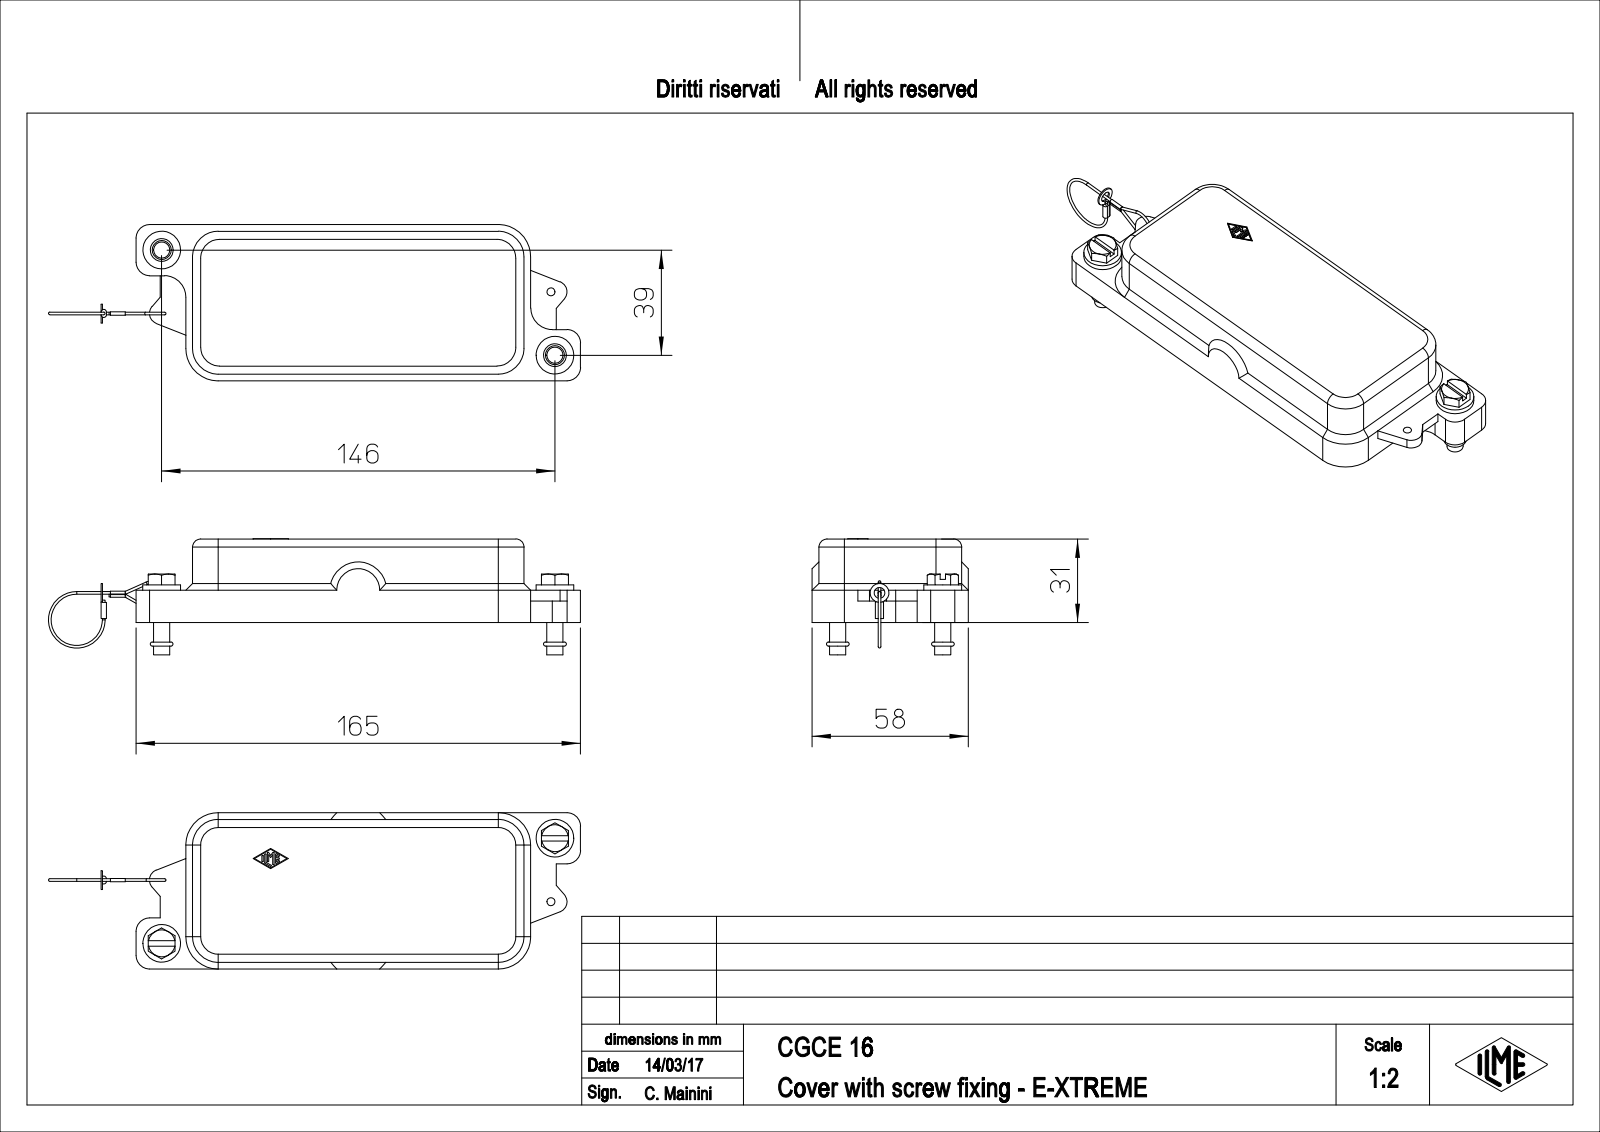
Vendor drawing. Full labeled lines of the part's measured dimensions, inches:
Part name (STEP PRODUCT): CGCE_16
STEP written by: PTC Creo Elements/Direct Modeling 19.0E 27-Jun-2016 (C) Parametric Technology GmbH (AUTOMOTIVE_DESIGN)
Units: inches
Bodies: 1 solid, 247 faces (124 planar, 87 cylindrical, 36 other)
Overall size (bounding box): 7.776 × 2.283 × 1.697
Volume: 4.996 in³ · Surface area: 59.37 in²
Round holes (diameter × count): ⌀0.276 ×2, ⌀0.551 ×2, ⌀0.118 ×1, ⌀0.157 ×1
Round bosses / shafts (diameter × count): ⌀0.039 ×5, ⌀0.236 ×2, ⌀0.217 ×2, ⌀0.276 ×1
Partial cylindrical surfaces — rounded edges, fillets, slot ends (radius × count): R0.01 ×14, R0.118 ×4, R0.197 ×4, R0.276 ×4, R0.374 ×4, R0.024 ×2, R0.039 ×2, R0.157 ×2
Main face-to-face distances: 0.276, 0.118, 0.098, 0.217, 2.185, 2.067, 1.969, 2.087, 0.472, 2.283
Hole centre spacings: 0.927, 5.722, 5.95
